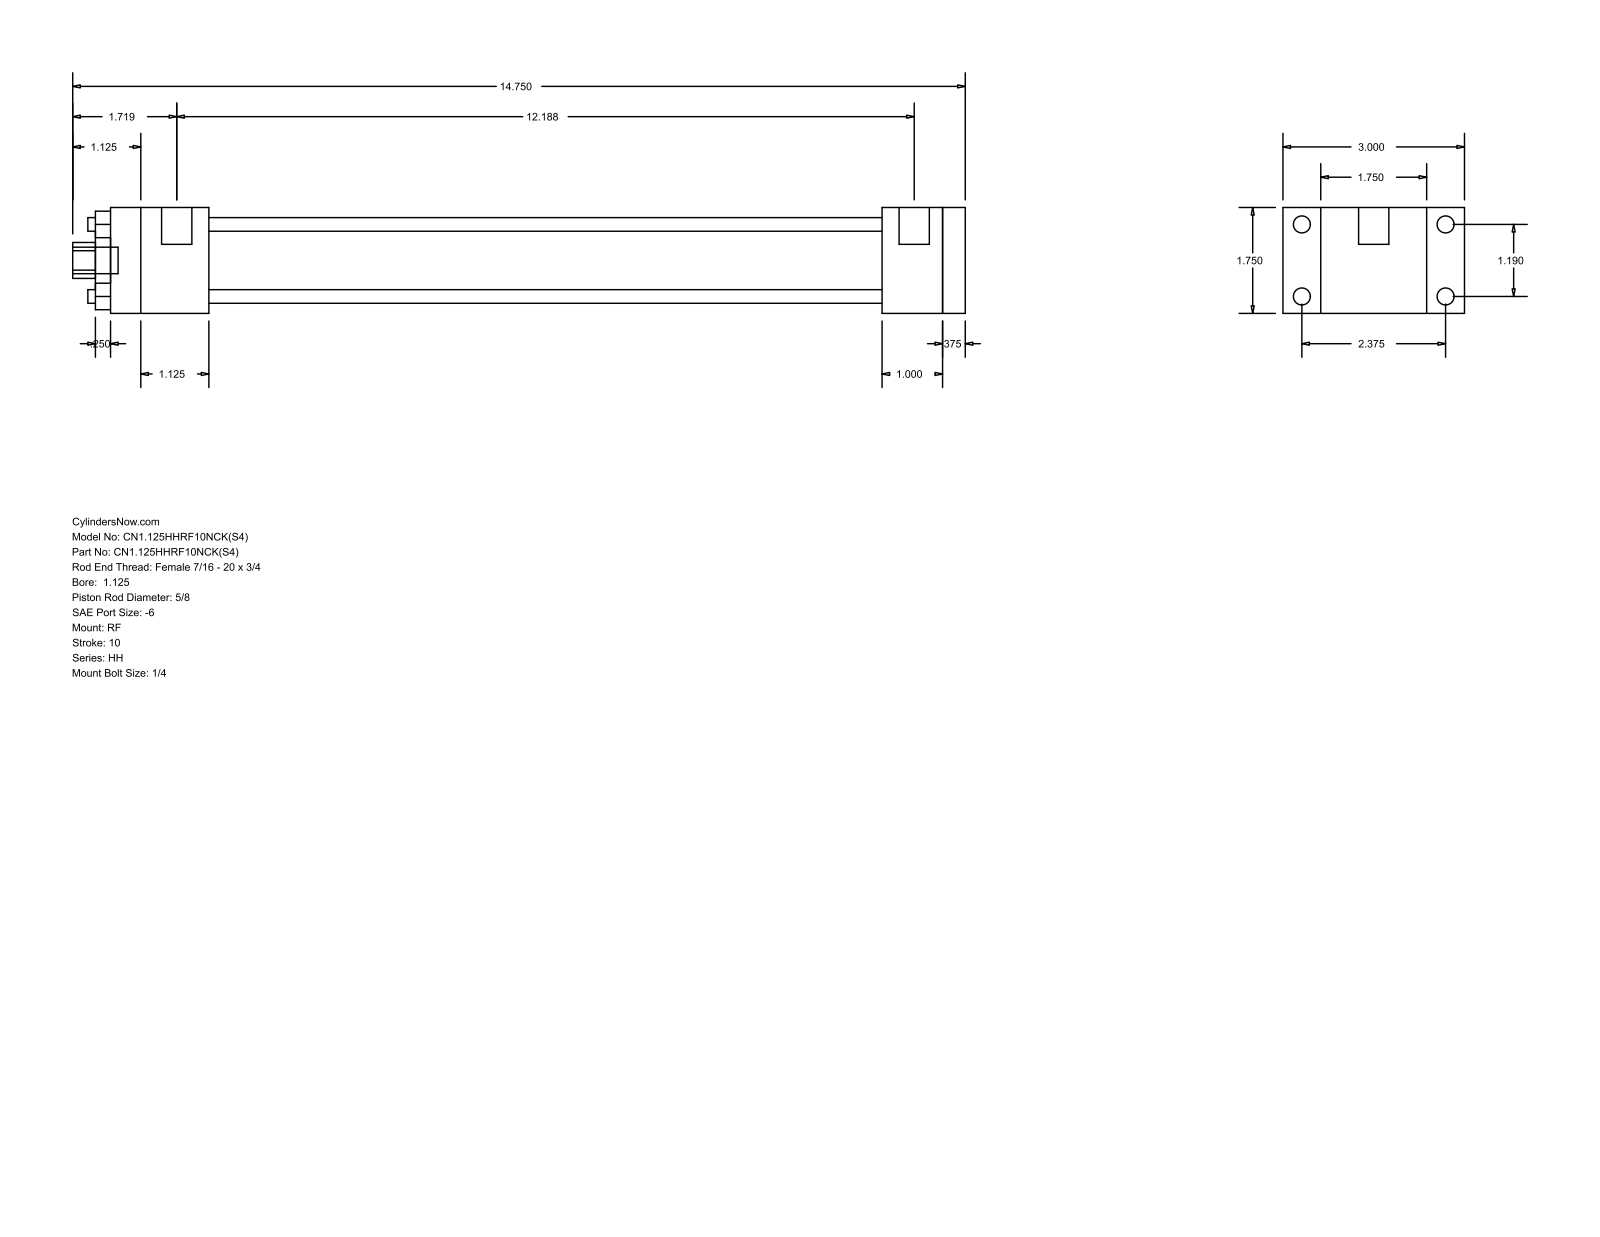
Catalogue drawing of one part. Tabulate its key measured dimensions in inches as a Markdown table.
| quantity | value |
| --- | --- |
| part name | HH_RF__0112_0.625 |
| STEP written by | GSSL Pune (CONFIG_CONTROL_DESIGN) |
| units | inches |
| bodies | 0 solids, 92 faces (64 planar, 28 cylindrical, 0 other) |
| overall size | 14.75 × 3 × 1.75 |
| round holes (diameter × count) | 0.225 × 4, 0.625 × 1, 1.125 × 1, 1.375 × 1 |
| round bosses / shafts (diameter × count) | 0.281 × 4, 0.219 × 4, 0.5 × 2, 0.437 × 1 |
| partial cylindrical surfaces (radius × count) | 0.297 × 1 |
| main face-to-face distances | 1.75, 0.375, 14.125, 0.625, 12.125, 12.5, 11.125, 1, 1.375, 1.625 |
| hole center spacings | 0.841, 1.19, 1.683 |
